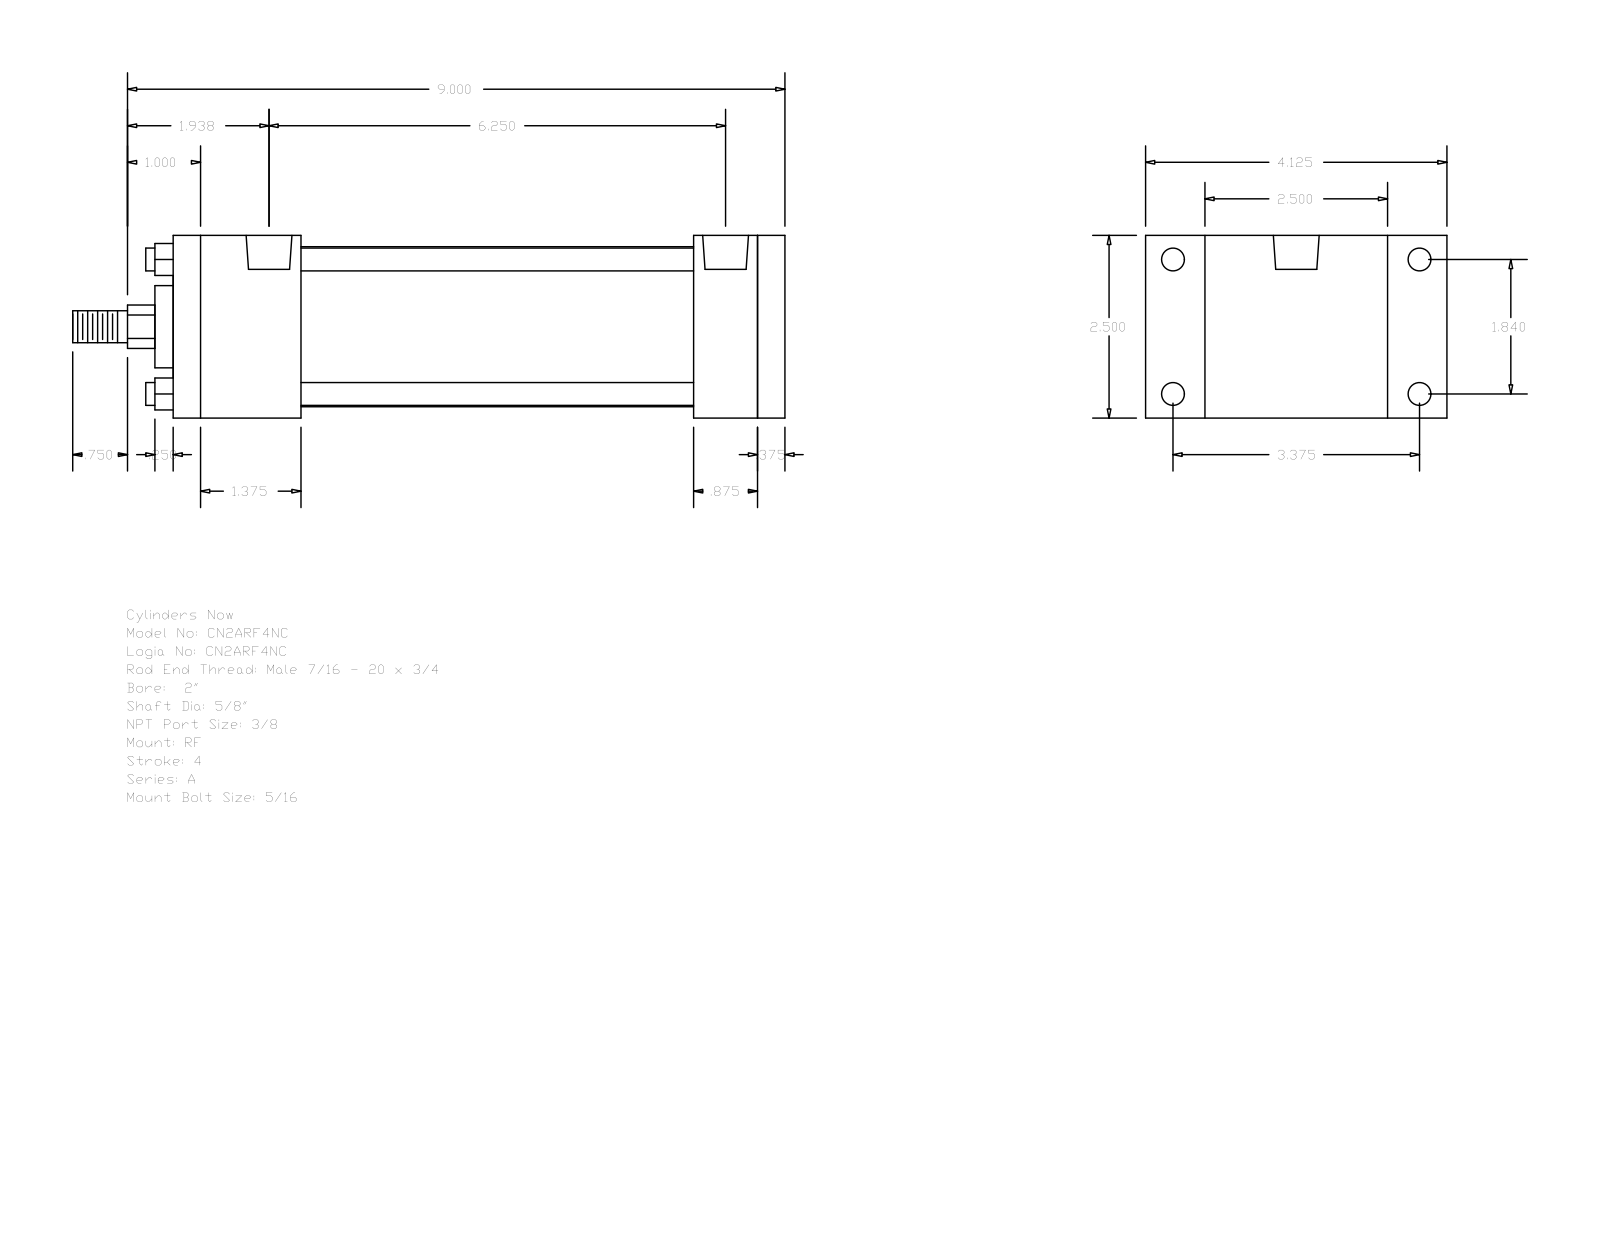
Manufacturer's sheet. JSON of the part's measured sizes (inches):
{"part_name": "A_RF__0200_0.625", "step_written_by": "GSSL Pune (CONFIG_CONTROL_DESIGN)", "units": "inches", "bodies": {"solids": 0, "faces": 92, "planar": 64, "cylindrical": 28, "other": 0}, "overall_size": [9.75, 4.125, 2.5], "round_holes": [[0.219, 4], [0.313, 4], [0.627, 2]], "round_bosses_or_shafts": [[0.313, 4], [2.19, 1], [1.125, 1], [0.625, 1], [0.437, 1]], "partial_cylinders_radius": [[0.297, 1]], "face_to_face_distances": [2.5, 8.375, 0.375, 8, 1.75, 6.25, 6.625, 7.125, 5.375, 0.875], "hole_center_spacings": [1.84, 3.375, 3.844, 5.937, 0.156, 0.157, 6.093, 6.094]}
